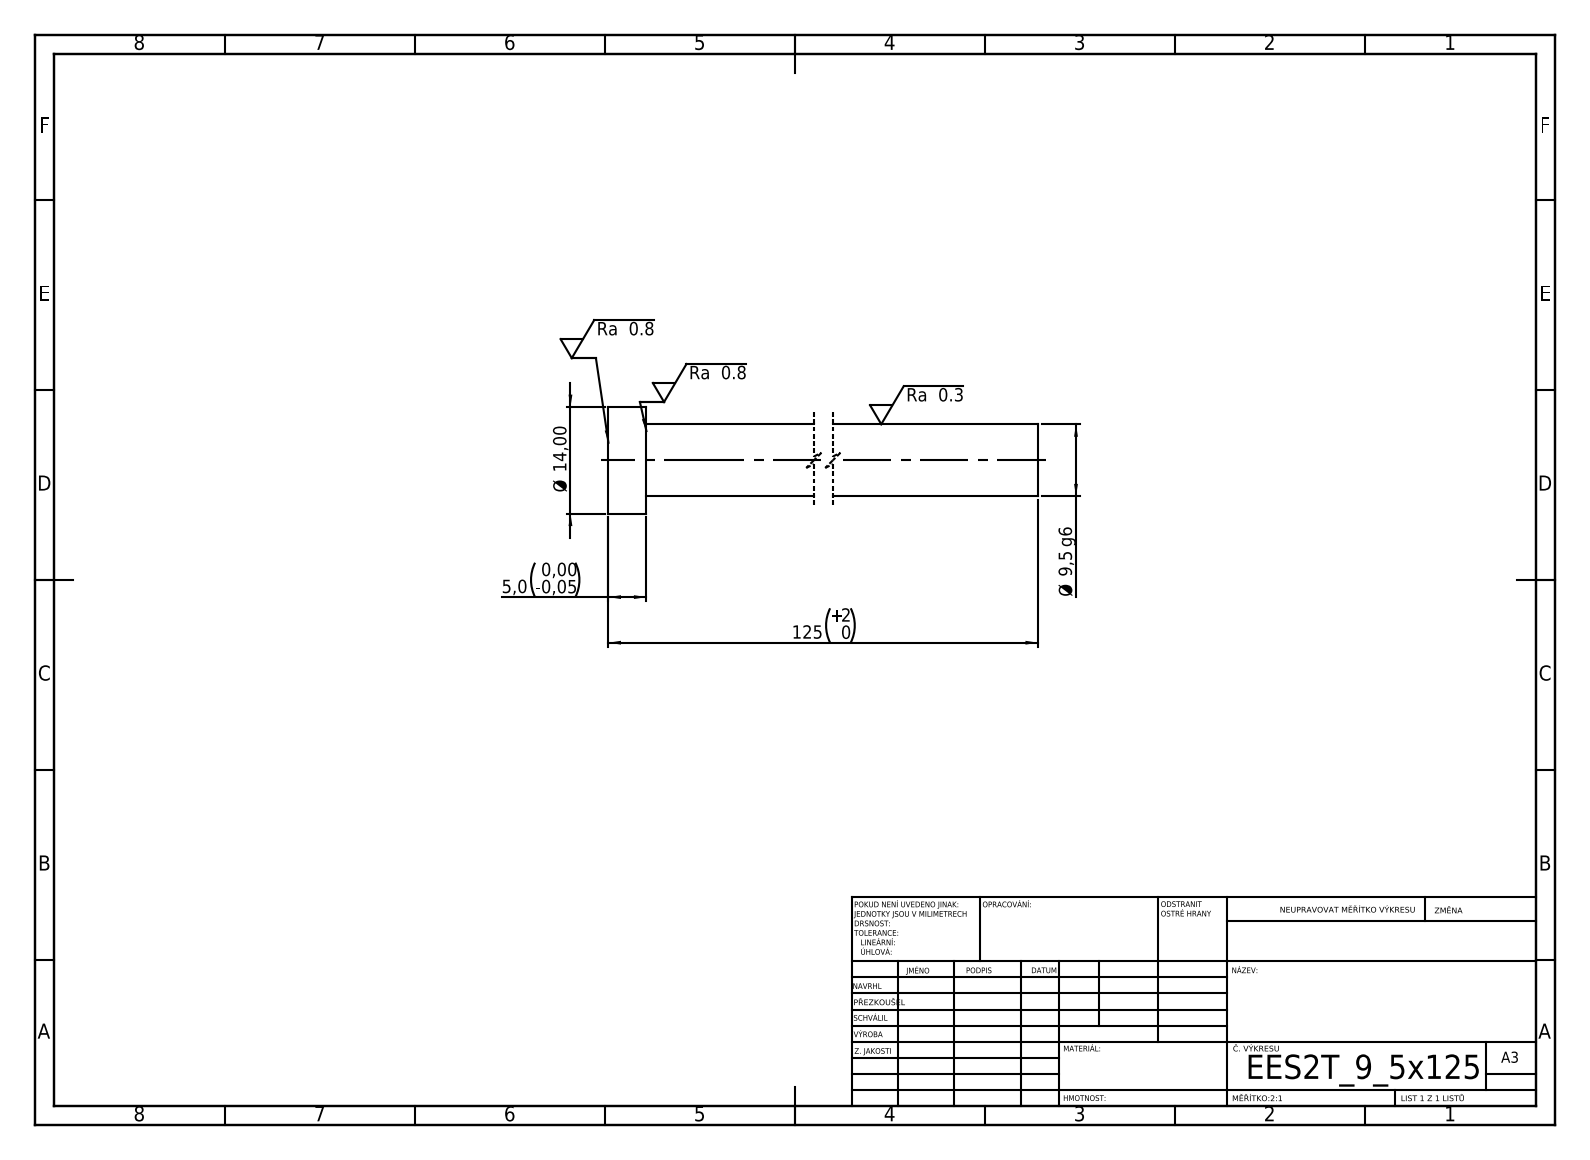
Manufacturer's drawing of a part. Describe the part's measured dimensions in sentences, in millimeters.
Its 3-D file was written by "SolidWorks 2019 (CONFIG_CONTROL_DESIGN)". It is 1 solid with 7 faces: 3 planar, 4 cylindrical and 0 other. Overall it measures 125 by 14 by 14 millimeters. Its volume is 9 276 cubic millimeters and its surface area 4 109 square millimeters. Round bosses or shafts: 1 of diameter 14, 1 of diameter 9.5. The main face-to-face distances are 5, 125, 120.
